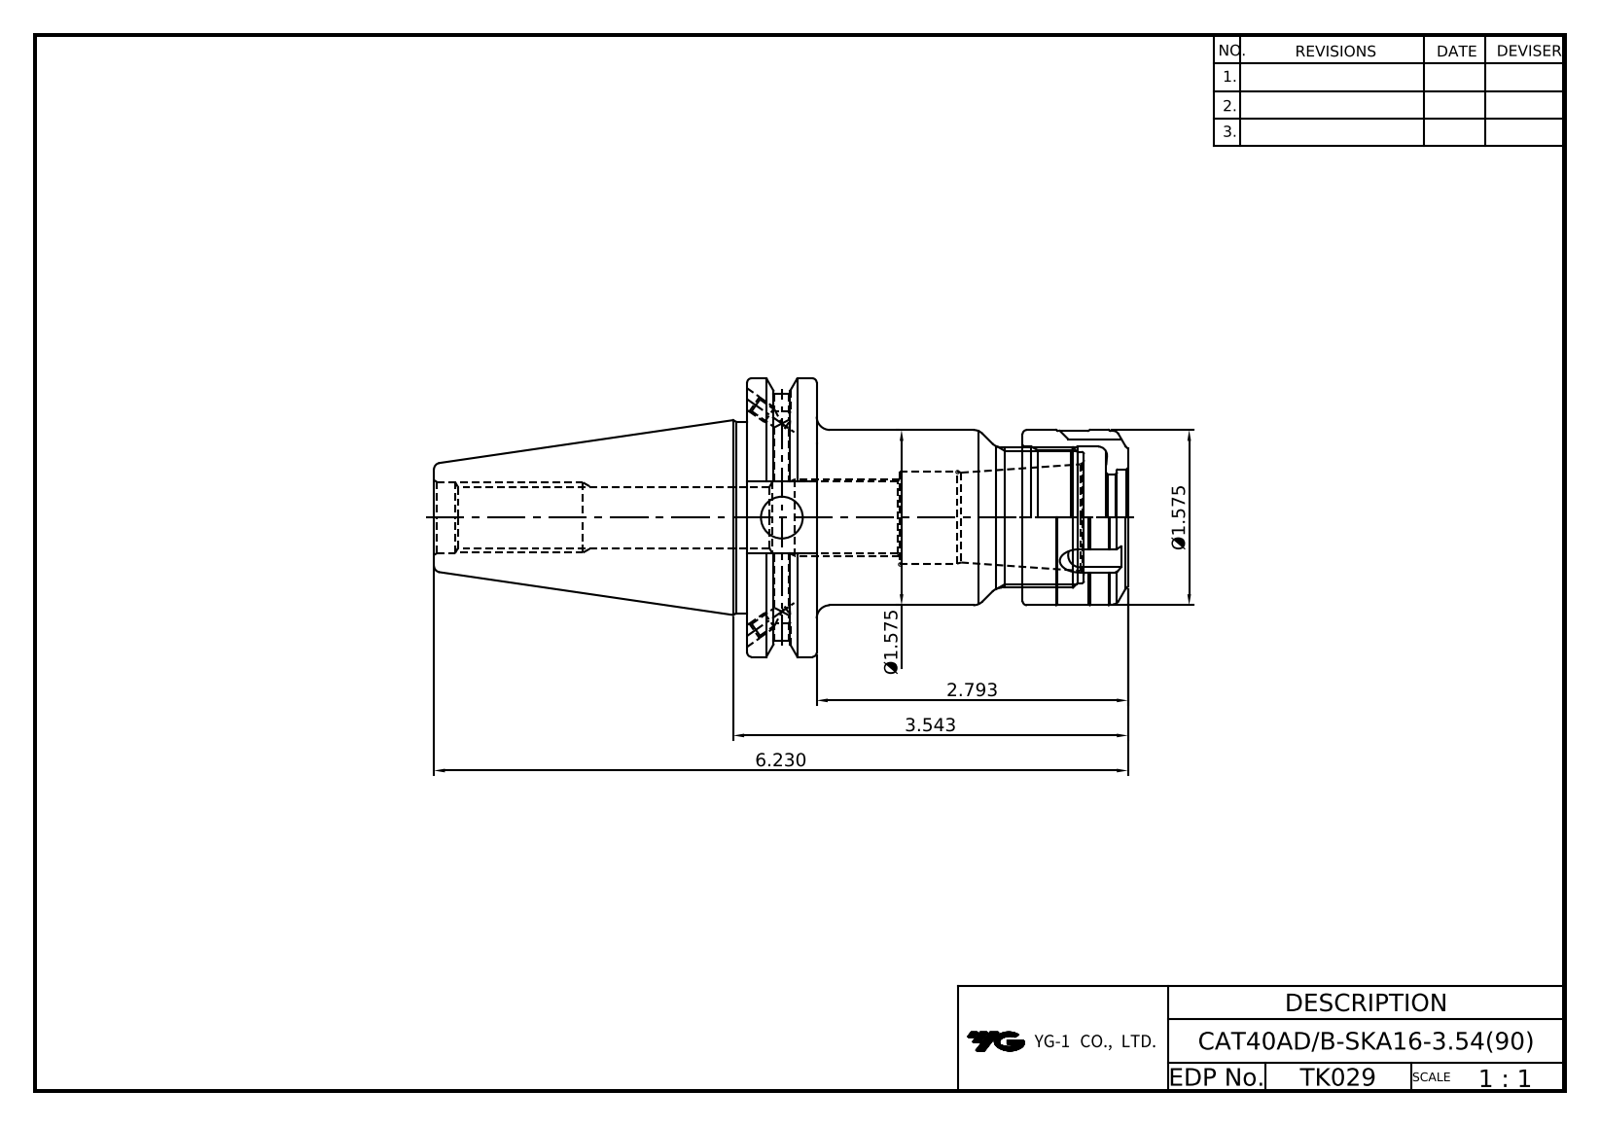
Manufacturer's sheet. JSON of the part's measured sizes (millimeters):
{"part_name": "LO-CAT40ADB-SKA16-90; SKN16-NUT", "step_written_by": "Autodesk Inventor 2025 (AP242_MANAGED_MODEL_BASED_3D_ENGINEERING_MIM_LF)", "units": "millimeters", "bodies": {"solids": 2, "faces": 155, "planar": 58, "cylindrical": 47, "other": 50}, "overall_size": [158.25, 63.5, 61.09], "volume_mm3": 158430, "surface_area_mm2": 38324, "round_holes": [[3.24, 4], [4, 2], [4.2, 2], [9.53, 1], [13.39, 1], [15.75, 1], [16.3, 1], [19.8, 1], [21, 1], [22, 1], [32, 1], [32.4, 1]], "round_bosses_or_shafts": [[63.5, 1], [43.6, 1], [40, 1], [39.6, 1]], "partial_cylinders_radius": [[28.15, 1]], "face_to_face_distances": [15.88, 81.93, 66.05, 86.83, 70.95, 4.9, 76.83, 60.95, 5.1, 10]}
